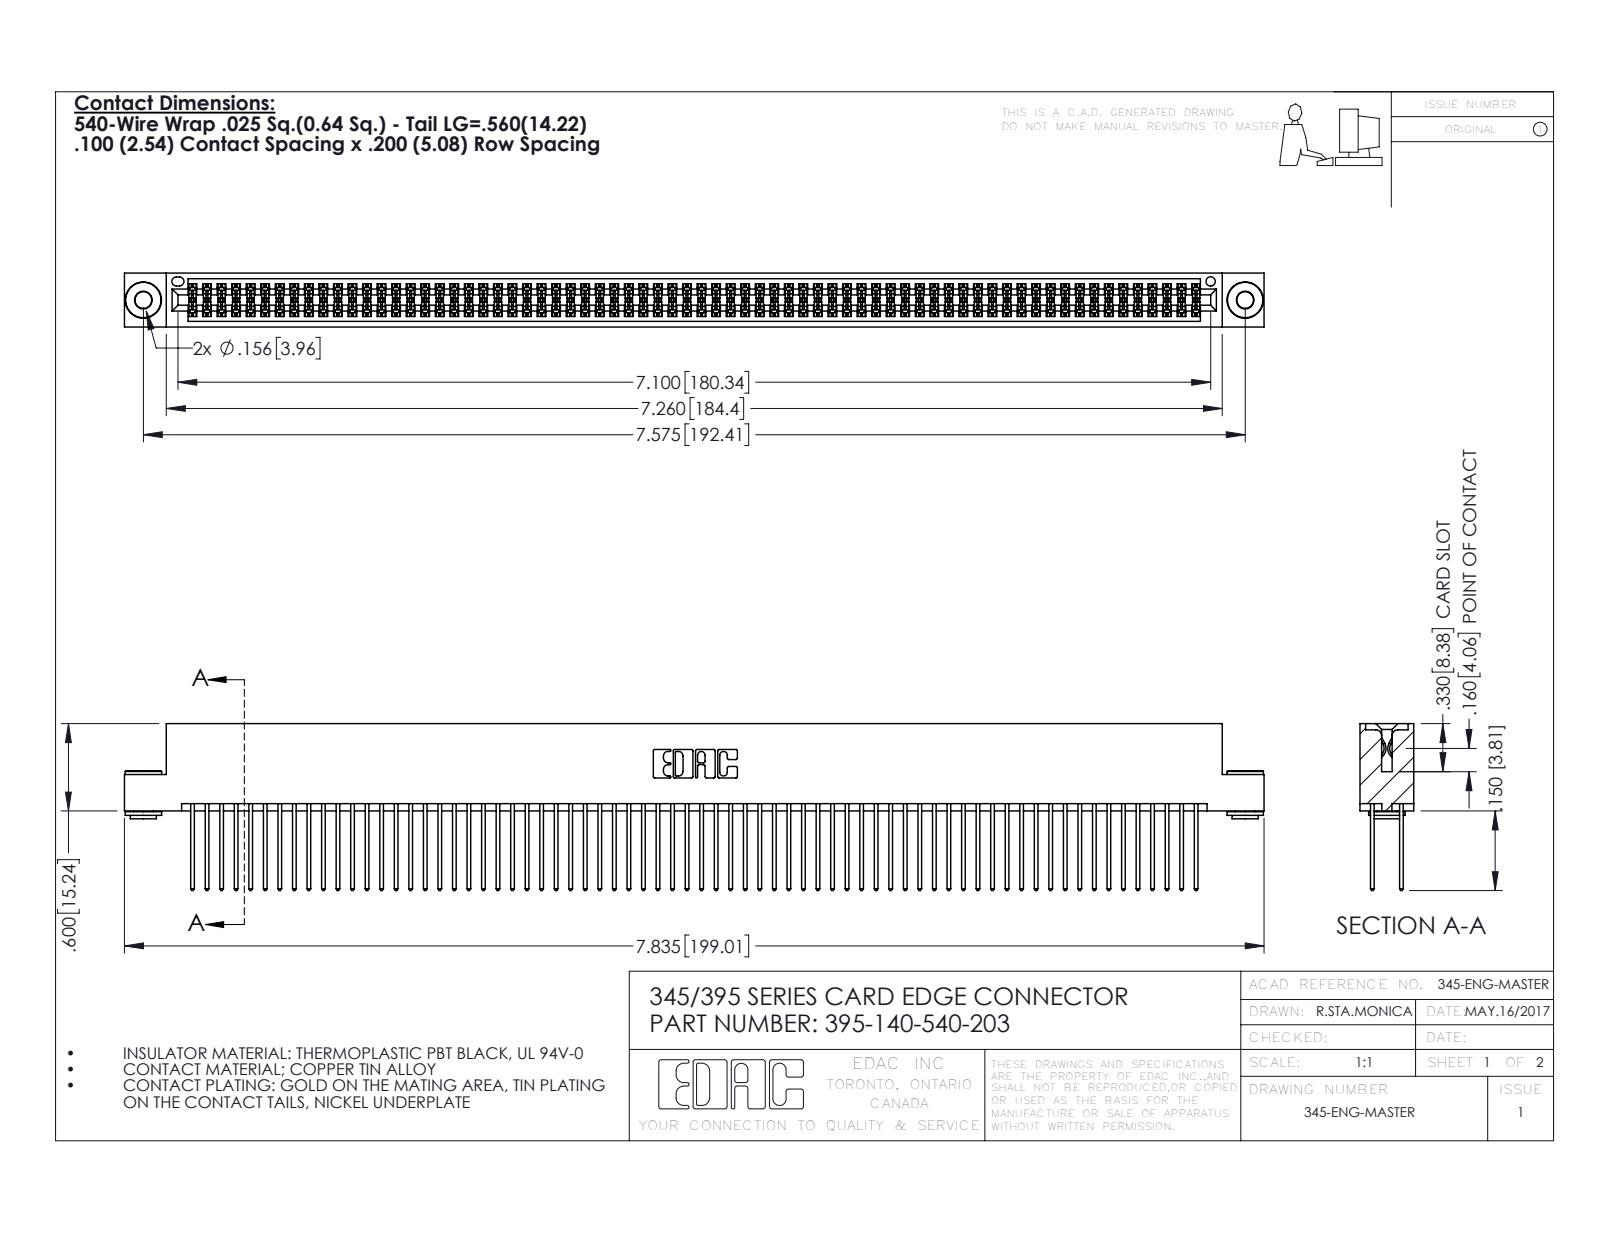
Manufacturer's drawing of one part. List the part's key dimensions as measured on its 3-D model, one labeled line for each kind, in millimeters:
Part name (STEP PRODUCT): 345-250-002_345-250-002-102; 345 Part_Flush Mounting Lugs - 0.156 Dia-TH; 395-140-540-203; 345-292-001_345-293-140
STEP written by: SolidWorks 2016 (CONFIG_CONTROL_DESIGN)
Units: millimetres
Bodies: 143 solids, 7164 faces (4710 planar, 2446 cylindrical, 8 other)
Overall size (bounding box): 199 × 29.1 × 9.4
Volume: 20 140 mm³ · Surface area: 32 980 mm²
Round holes (diameter × count): ⌀2.9 ×2, ⌀4 ×2, ⌀1.6 ×1
Round bosses / shafts (diameter × count): ⌀6.4 ×2, ⌀4.6 ×2, ⌀3.5 ×2
Partial cylindrical surfaces — rounded edges, fillets, slot ends (radius × count): R0.2 ×210, R0.3 ×140, R0.3 ×22, R0.2 ×6, R0.8 ×6, R0.7 ×3, R0.4 ×2, R0.5 ×2
Main face-to-face distances: 1.8, 7.6, 5.1, 0.6, 2.5, 6.9, 5.7, 9.4, 4.4, 3.8
Hole centre spacings: 6.9, 186.4, 192.4
